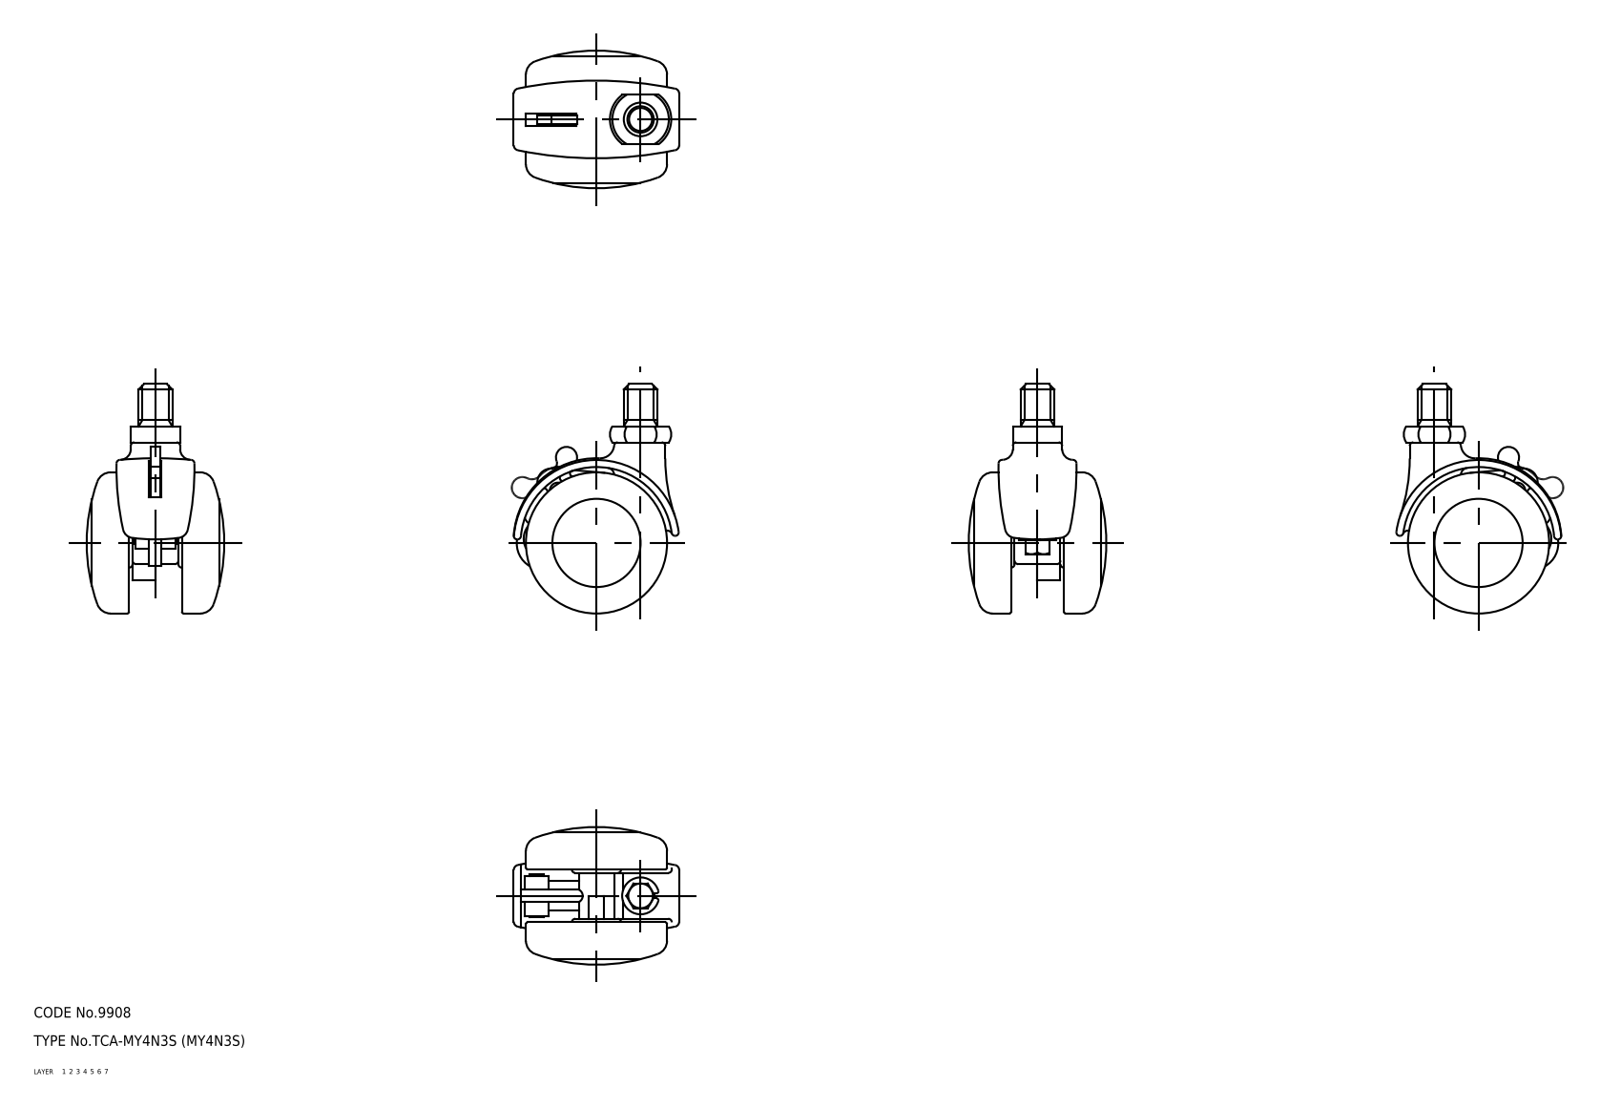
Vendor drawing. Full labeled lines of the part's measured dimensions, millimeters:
Part name (STEP PRODUCT): wheel; main shaft; lever; MY4N3S_14640_36
STEP written by: CADfix (AUTOMOTIVE_DESIGN)
Units: millimetres
Bodies: 6 solids, 199 faces (0 planar, 0 cylindrical, 199 other)
Overall size (bounding box): 65 × 47.81 × 39
Volume: 30 339 mm³ · Surface area: 20 112 mm²
